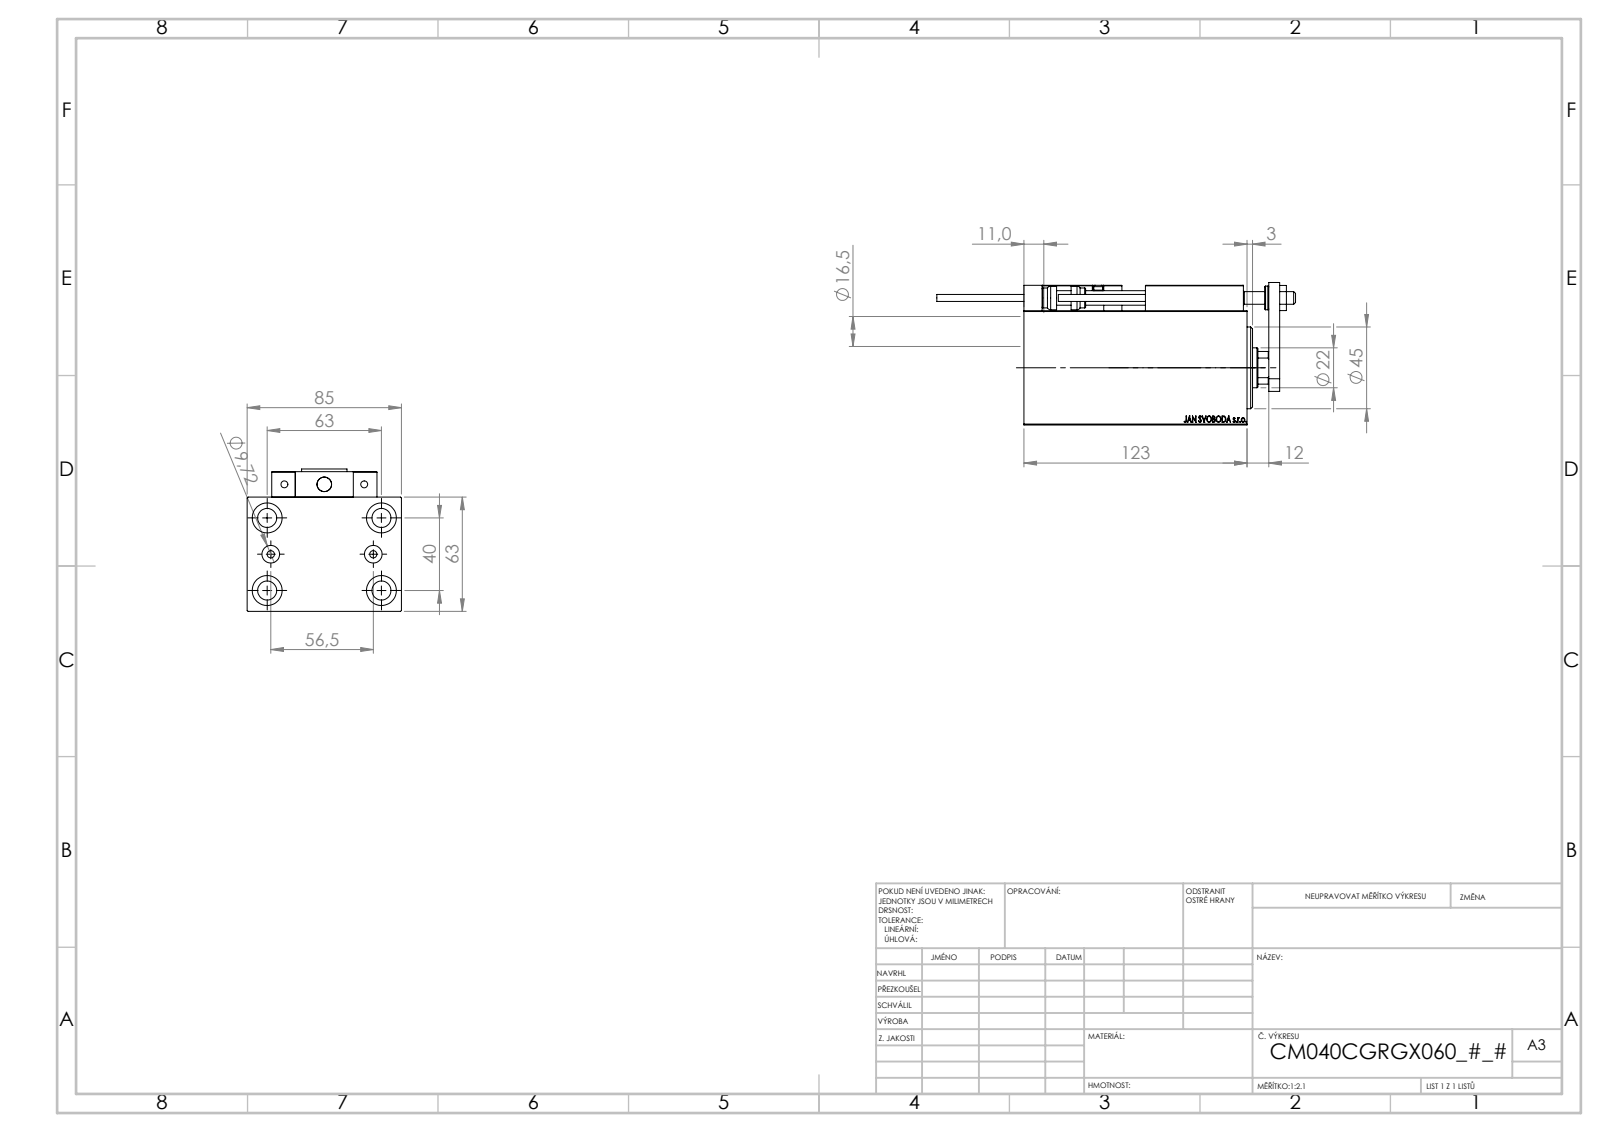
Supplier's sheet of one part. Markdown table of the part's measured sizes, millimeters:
| quantity | value |
| --- | --- |
| part name | ZARAZKA; V450CM_C_Body; NUT_D12; TYC_L79 (+7 more) |
| STEP written by | SolidWorks 2019 (CONFIG_CONTROL_DESIGN) |
| units | millimeters |
| bodies | 23 solids, 1278 faces (560 planar, 184 cylindrical, 534 other) |
| overall size | 197.7 × 85 × 78.5 |
| volume | 603 352 mm³ |
| surface area | 126 539 mm² |
| round holes (diameter × count) | 4 × 6, 8 × 5, 16.5 × 5, 3.2 × 4, 10.5 × 4, 5 × 2, 9.72 × 2, 7 × 1, 12.5 × 1, 22 × 1, 25.5 × 1, 40 × 1 |
| round bosses / shafts (diameter × count) | 5 × 2, 3.8 × 2, 13 × 1, 11 × 1 |
| partial cylindrical surfaces (radius × count) | 0.3 × 30, 3 × 2, 10.5 × 1 |
| main face-to-face distances | 63, 85, 12, 111, 123, 14, 77, 15, 18, 30 |
| hole center spacings | 37.31, 11.37, 20, 20.1, 20.5, 29.59, 29.69, 36.06 |
